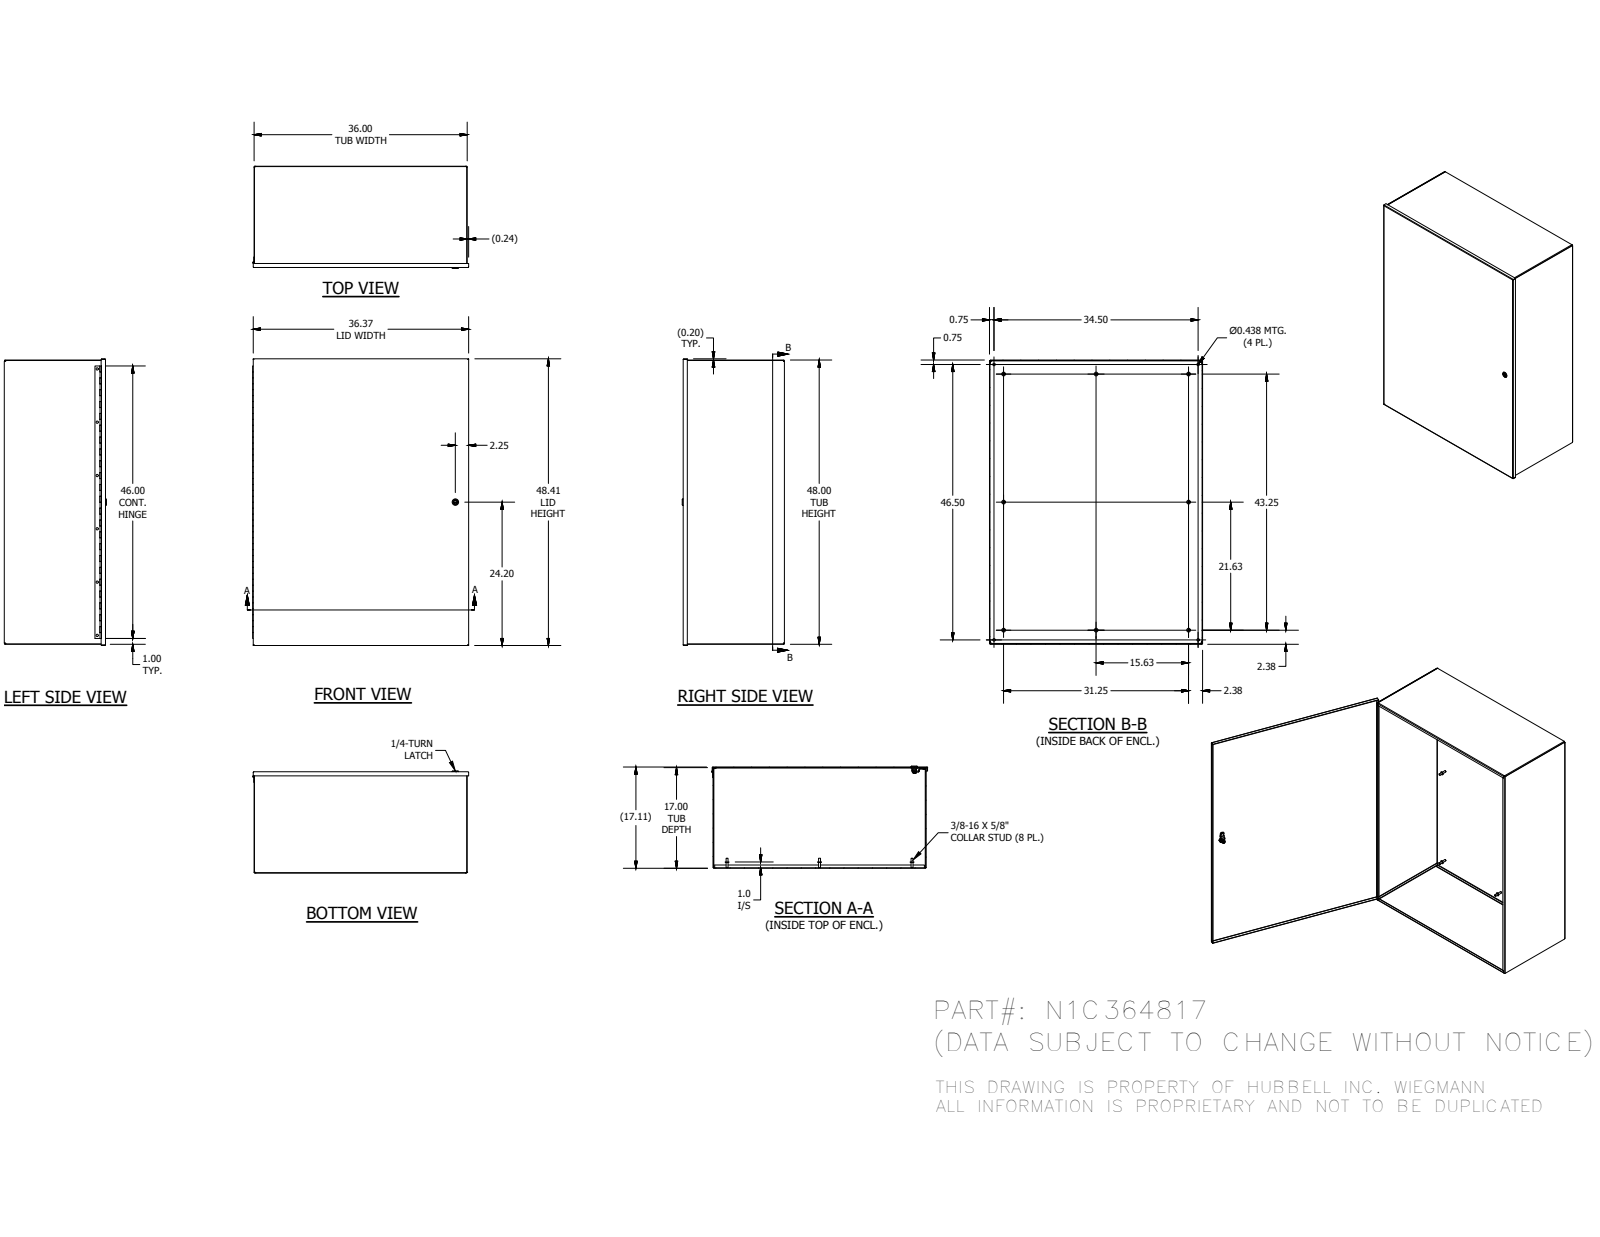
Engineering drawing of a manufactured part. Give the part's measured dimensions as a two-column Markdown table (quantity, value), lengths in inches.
| quantity | value |
| --- | --- |
| part name | N1C364817BLR; N1C3617TB; N1C3648LID; 1000-101-GPF_GPD (+8 more) |
| STEP written by | Autodesk Inventor 2016 (AUTOMOTIVE_DESIGN) |
| units | inches |
| bodies | 22 solids, 1042 faces (681 planar, 291 cylindrical, 70 other) |
| overall size | 48.406 × 36.489 × 17.263 |
| volume | 492.4 in³ |
| surface area | 13 380 in² |
| round holes (diameter × count) | 0.375 × 6, 0.437 × 4, 0.125 × 1, 0.197 × 1, 0.315 × 1, 0.394 × 1, 0.402 × 1, 0.634 × 1, 0.802 × 1 |
| round bosses / shafts (diameter × count) | 0.625 × 8, 0.33 × 8, 1.102 × 1, 1.063 × 1, 0.906 × 1, 0.78 × 1, 0.622 × 1, 0.598 × 1 |
| partial cylindrical surfaces (radius × count) | 0.012 × 30, 0.137 × 12, 0.063 × 11, 0.02 × 10, 0.031 × 4, 0.105 × 4, 0.157 × 4, 0.016 × 3 |
| main face-to-face distances | 0.074, 17.031, 16.957, 17.105, 35.926, 47.926, 35.852, 36, 47.852, 48 |
| hole center spacings | 9, 18, 27, 23.284, 34.5, 36, 40.563, 46.5 |
